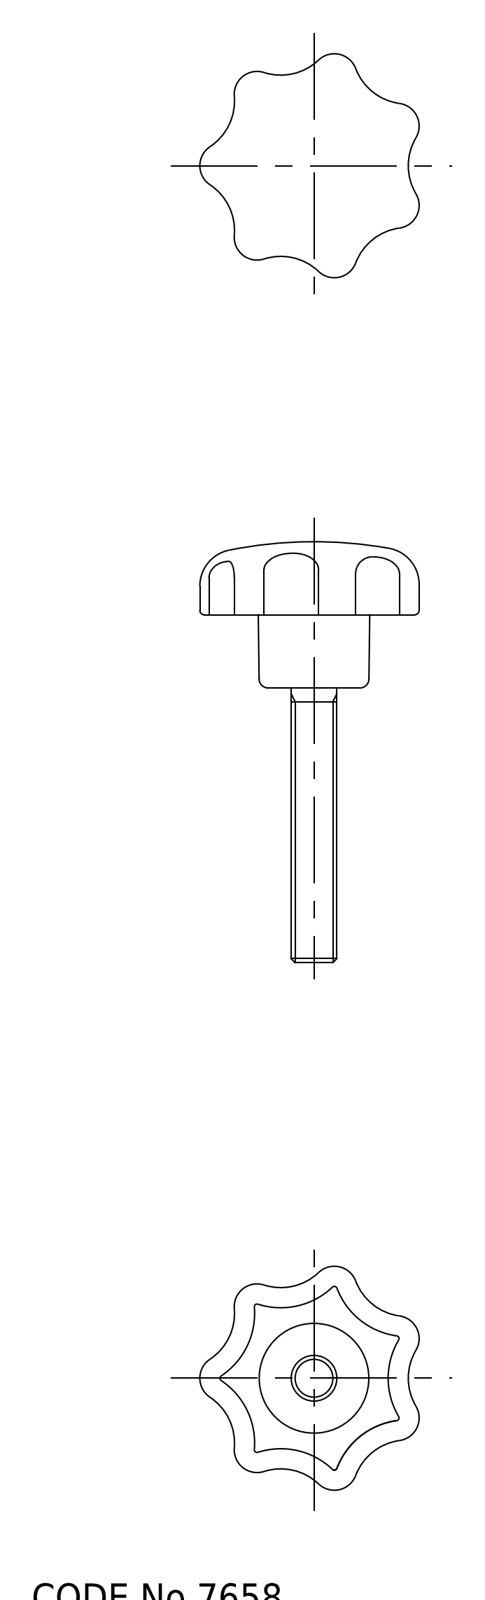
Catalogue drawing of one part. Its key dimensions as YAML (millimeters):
part_name: "screw; knob; KSM_25_M5_30_8884_36"
step_written_by: "CADfix (AUTOMOTIVE_DESIGN)"
units: millimeters
bodies: {solids: 2, faces: 125, planar: 0, cylindrical: 0, other: 125}
overall_size: [46, 24.5, 24.01]
volume: 3740
surface_area: 2939
